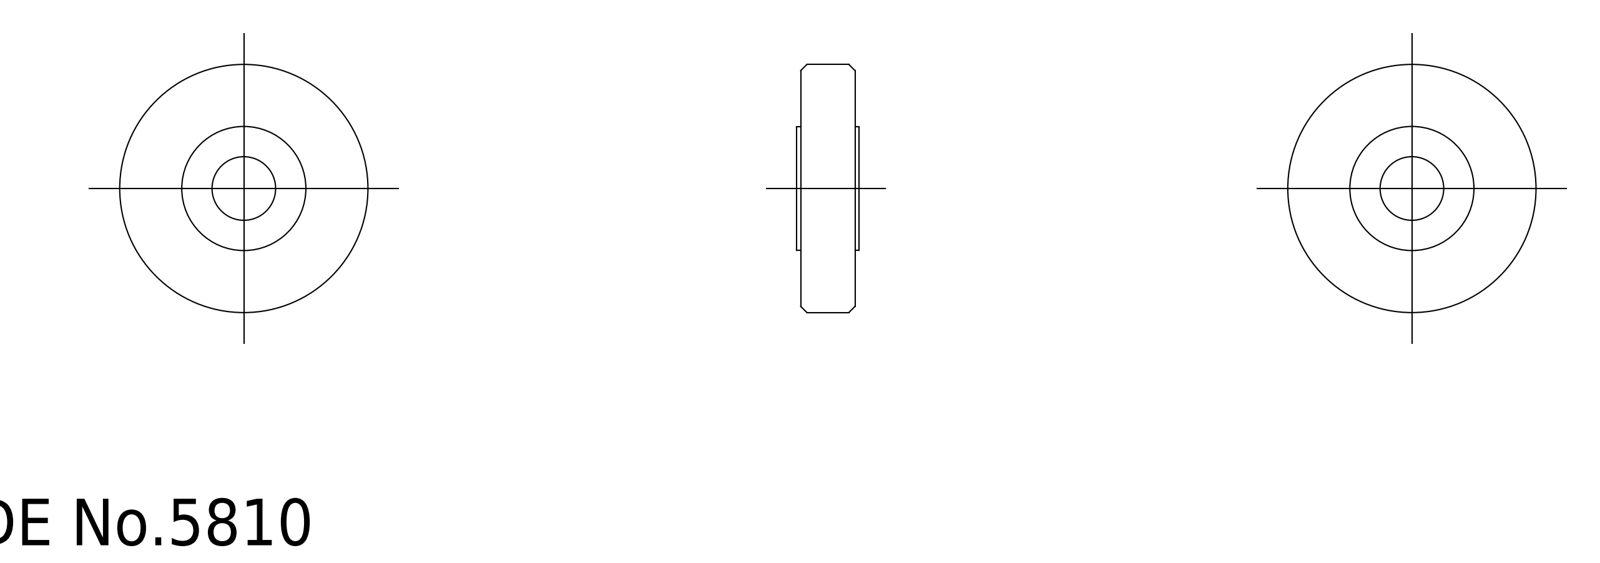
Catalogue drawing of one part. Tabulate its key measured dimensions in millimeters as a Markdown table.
| quantity | value |
| --- | --- |
| part name | roller |
| STEP written by | CADfix (AUTOMOTIVE_DESIGN) |
| units | millimeters |
| bodies | 1 solid, 22 faces (0 planar, 0 cylindrical, 22 other) |
| overall size | 16 × 16 × 4 |
| volume | 669 mm³ |
| surface area | 667 mm² |
